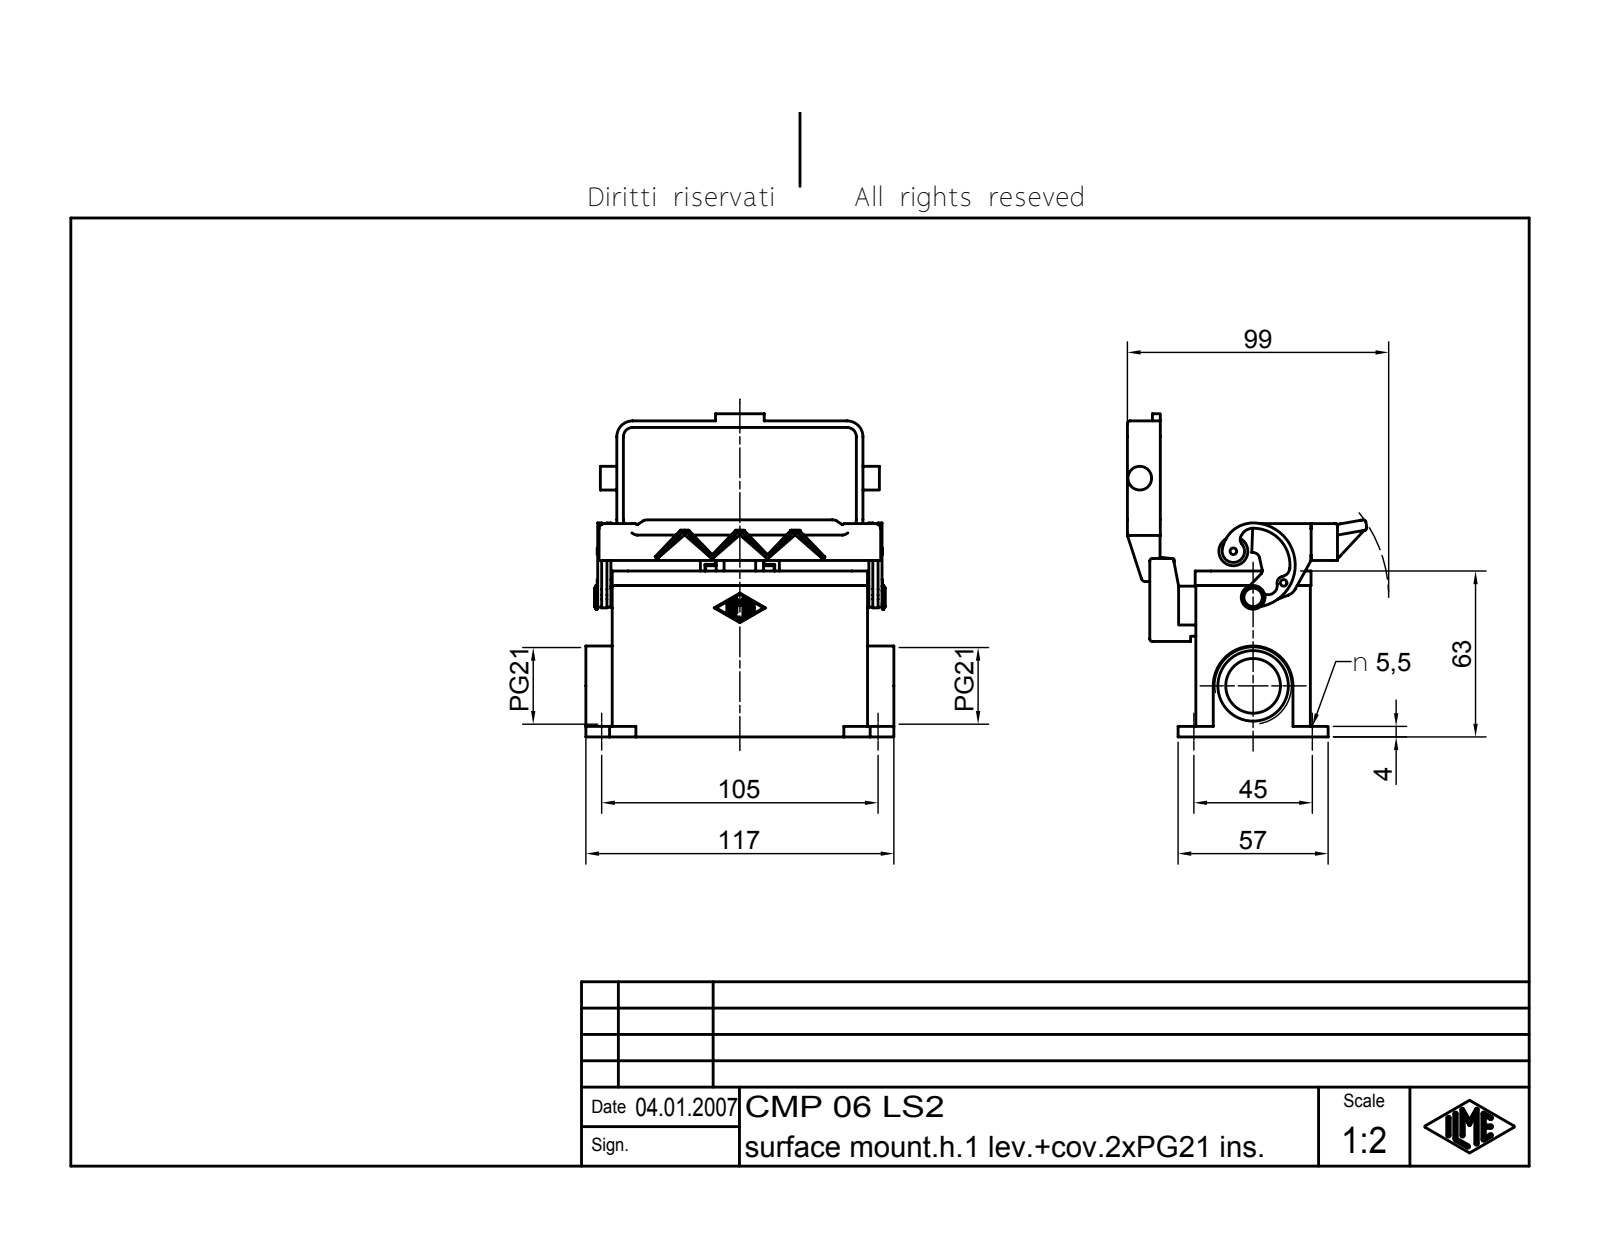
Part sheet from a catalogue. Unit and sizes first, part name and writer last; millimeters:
Units: millimetres
Overall size (bounding box): 122.7 × 117 × 90.95
Round holes (diameter × count): ⌀5.5 ×4, ⌀2 ×1, ⌀4 ×1, ⌀20.78 ×1, ⌀26.78 ×1
Round bosses / shafts (diameter × count): ⌀9 ×2, ⌀5 ×2, ⌀11 ×1, ⌀7 ×1, ⌀4 ×1, ⌀3 ×1, ⌀2.5 ×1
Partial cylindrical surfaces — rounded edges, fillets, slot ends (radius × count): R1 ×18, R0.38 ×14, R2 ×12, R6 ×12, R1.5 ×6, R3.5 ×6, R3 ×4, R0.5 ×3
Main face-to-face distances: 3, 40.5, 4, 43.5, 63, 37.5, 26, 66.5, 69.5, 29
Hole centre spacings: 45, 105, 114.24, 40.79
Volume: 140 409 mm³ · Surface area: 78 645 mm²
Bodies: 6 solids, 609 faces (265 planar, 180 cylindrical, 164 other)
Part name (STEP PRODUCT): CMP 06 LS2
STEP written by: Autodesk Inventor 7 (AUTOMOTIVE_DESIGN)
